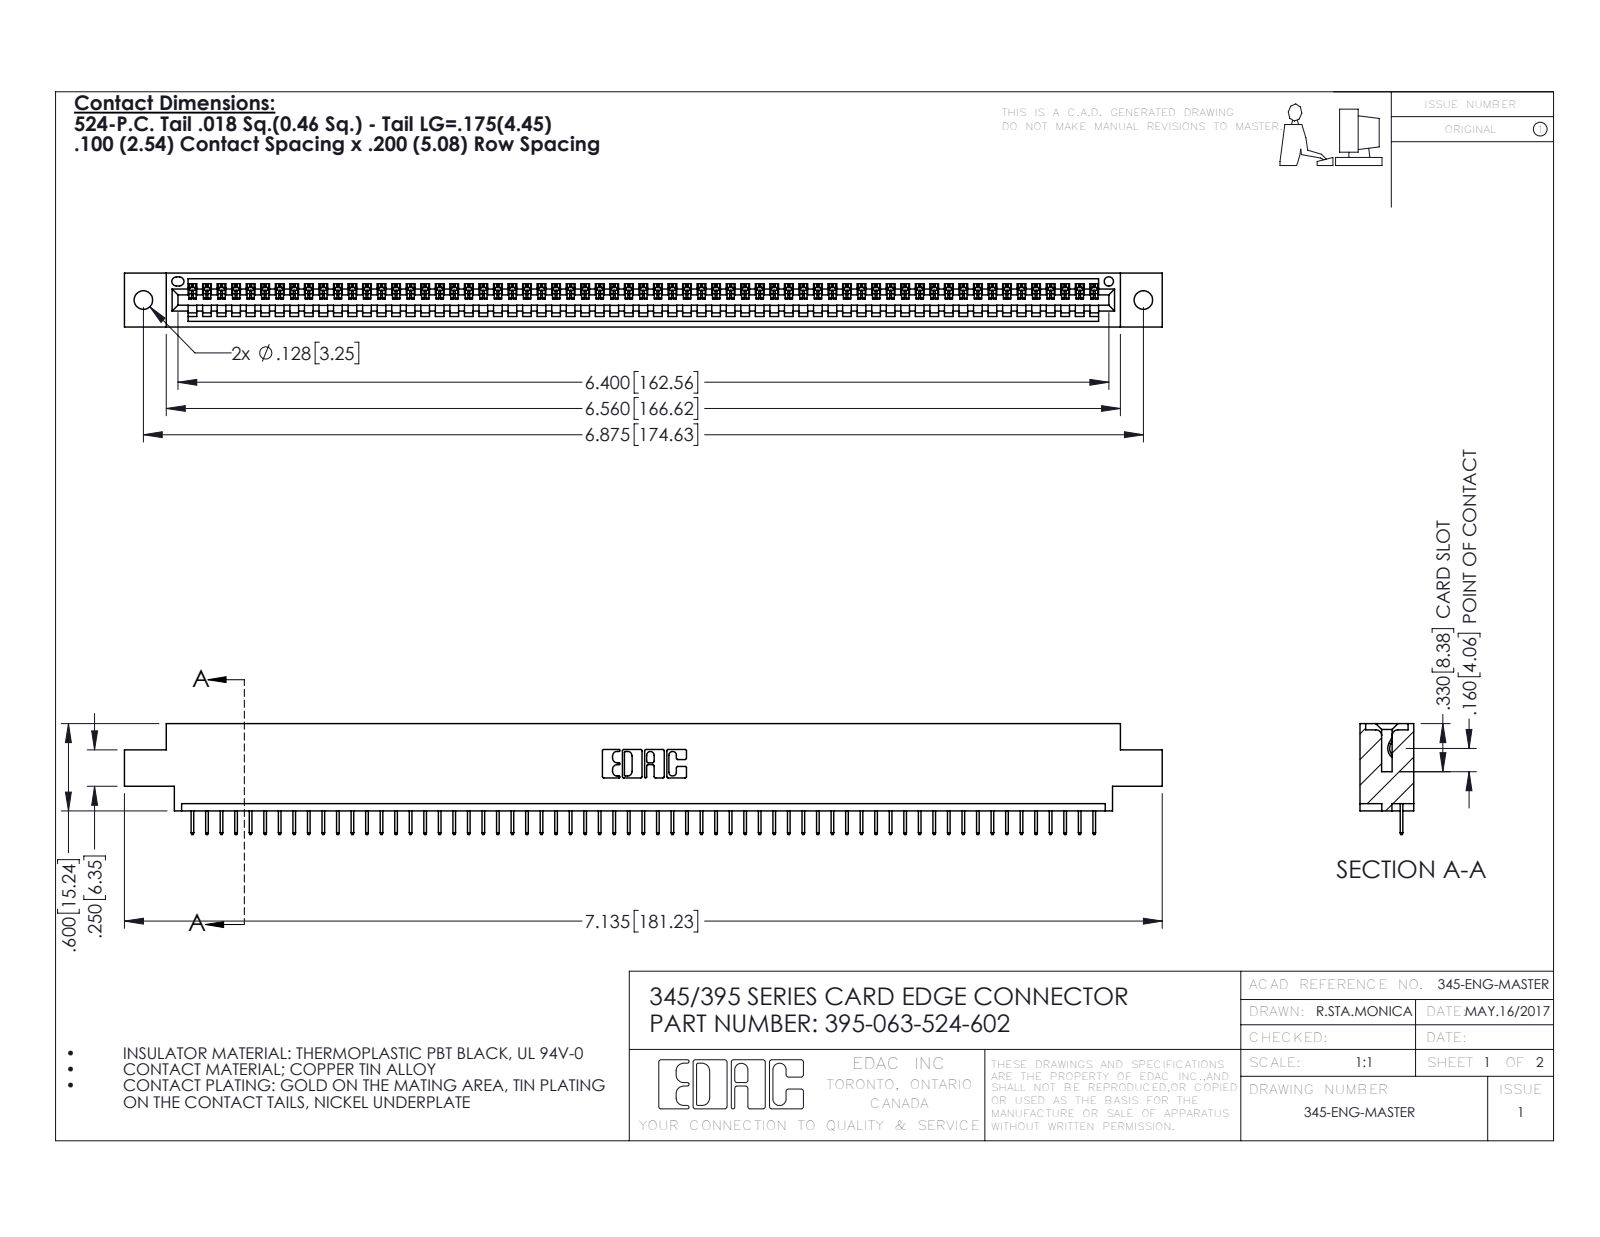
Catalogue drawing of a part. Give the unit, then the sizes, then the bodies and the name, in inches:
Units: inches
Overall size (bounding box): 7.135 × 0.762 × 0.37
Round holes (diameter × count): ⌀0.128 ×2, ⌀0.064 ×1
Partial cylindrical surfaces — rounded edges, fillets, slot ends (radius × count): R0.006 ×126, R0.01 ×22, R0.007 ×6, R0.031 ×6, R0.026 ×3, R0.031 ×2, R0.04 ×2, R0.014 ×1
Main face-to-face distances: 0.072, 0.298, 0.37, 0.2, 0.098, 0.272, 0.025, 0.225, 0.072, 0.175
Hole centre spacings: 0.27, 6.639, 6.875
Volume: 1.037 in³ · Surface area: 33.97 in²
Bodies: 64 solids, 4036 faces (2982 planar, 1054 cylindrical, 0 other)
Part name (STEP PRODUCT): 345-292-001_345-293-124; 345 Part_0.170 Offset - 0.128 Dia; 395-063-524-602
STEP written by: SolidWorks 2016 (CONFIG_CONTROL_DESIGN)
